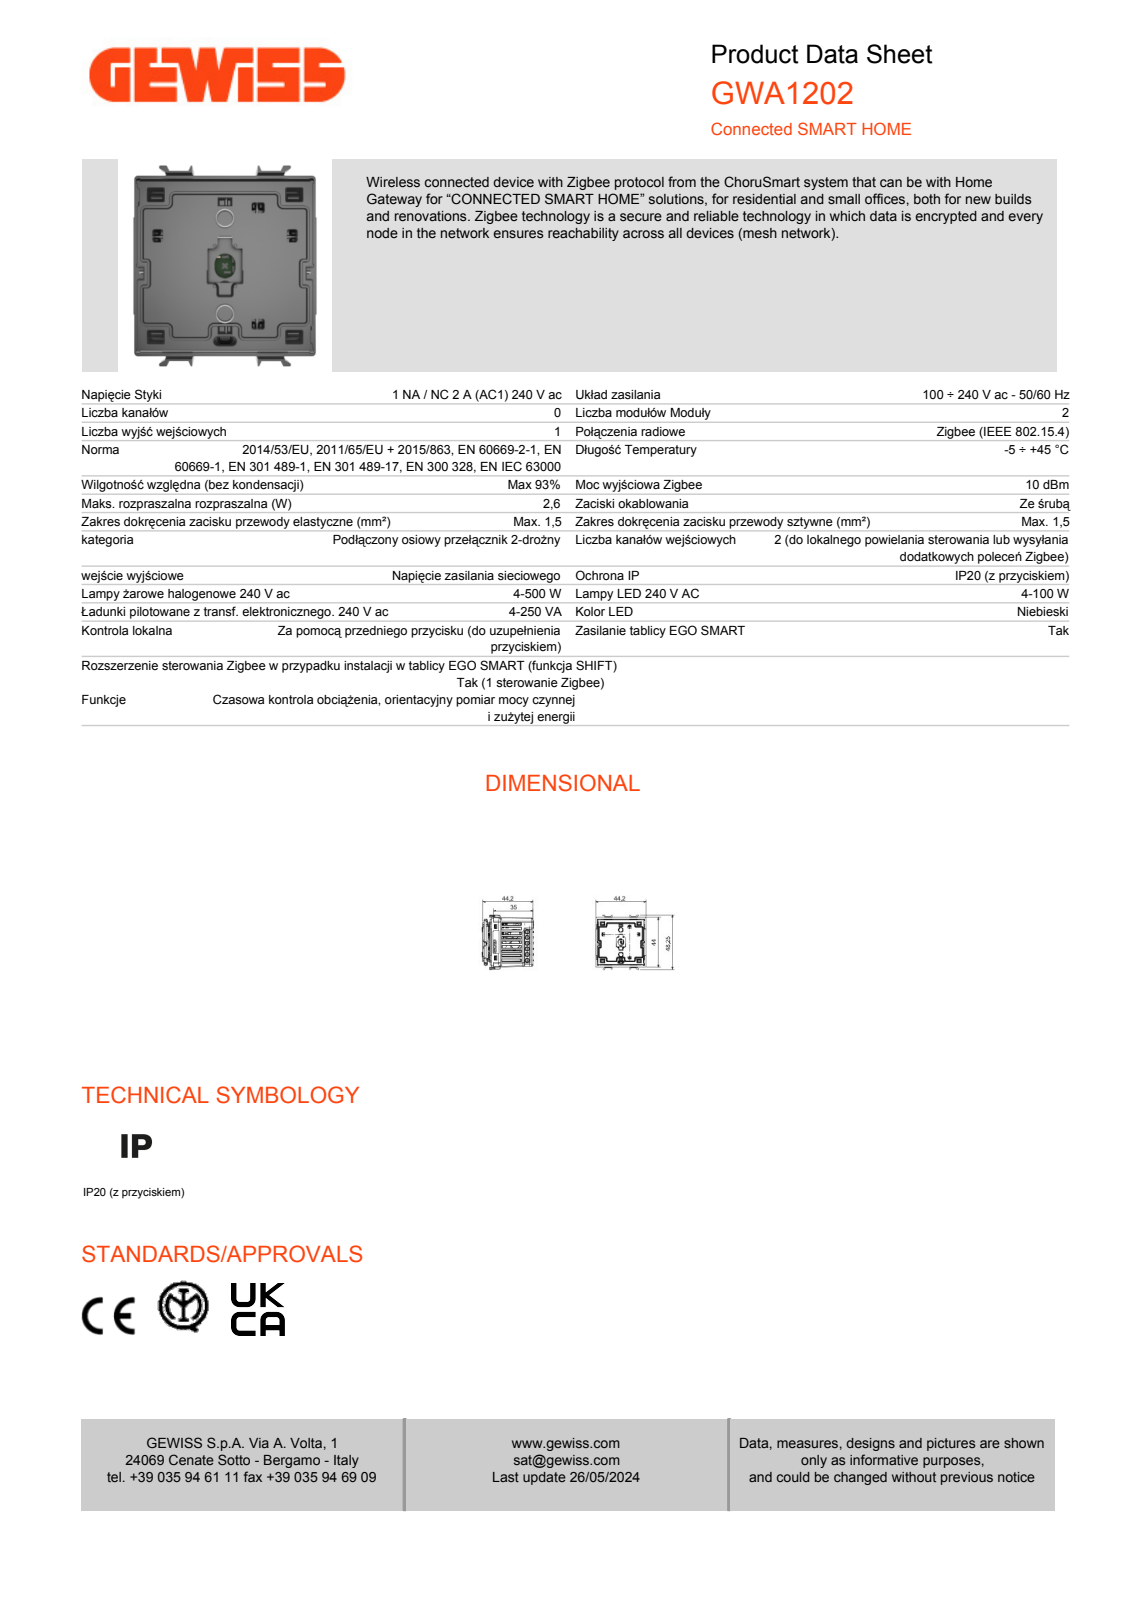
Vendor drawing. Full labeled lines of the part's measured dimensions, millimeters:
Part name (STEP PRODUCT): GWA1202
STEP written by: CATIA V5 STEP AP214 v1 (AUTOMOTIVE_DESIGN)
Units: millimetres
Bodies: 2 solids, 2679 faces (993 planar, 1020 cylindrical, 666 other)
Overall size (bounding box): 48.25 × 44.4 × 44.2
Volume: 42 331 mm³ · Surface area: 17 350 mm²
Round holes (diameter × count): ⌀3 ×6, ⌀1.99 ×2, ⌀2.5 ×1
Partial cylindrical surfaces — rounded edges, fillets, slot ends (radius × count): R0.2 ×306, R0.1 ×133, R0.5 ×128, R0.3 ×84, R1.7 ×35, R1 ×21, R1.2 ×14, R0.9 ×4
Main face-to-face distances: 1.5, 1.3, 5.2, 3.9, 6.7, 1, 6.4, 5.4, 4.9, 41.7
Hole centre spacings: 5, 10, 15, 20, 8.39, 9.14, 9.26, 9.68
